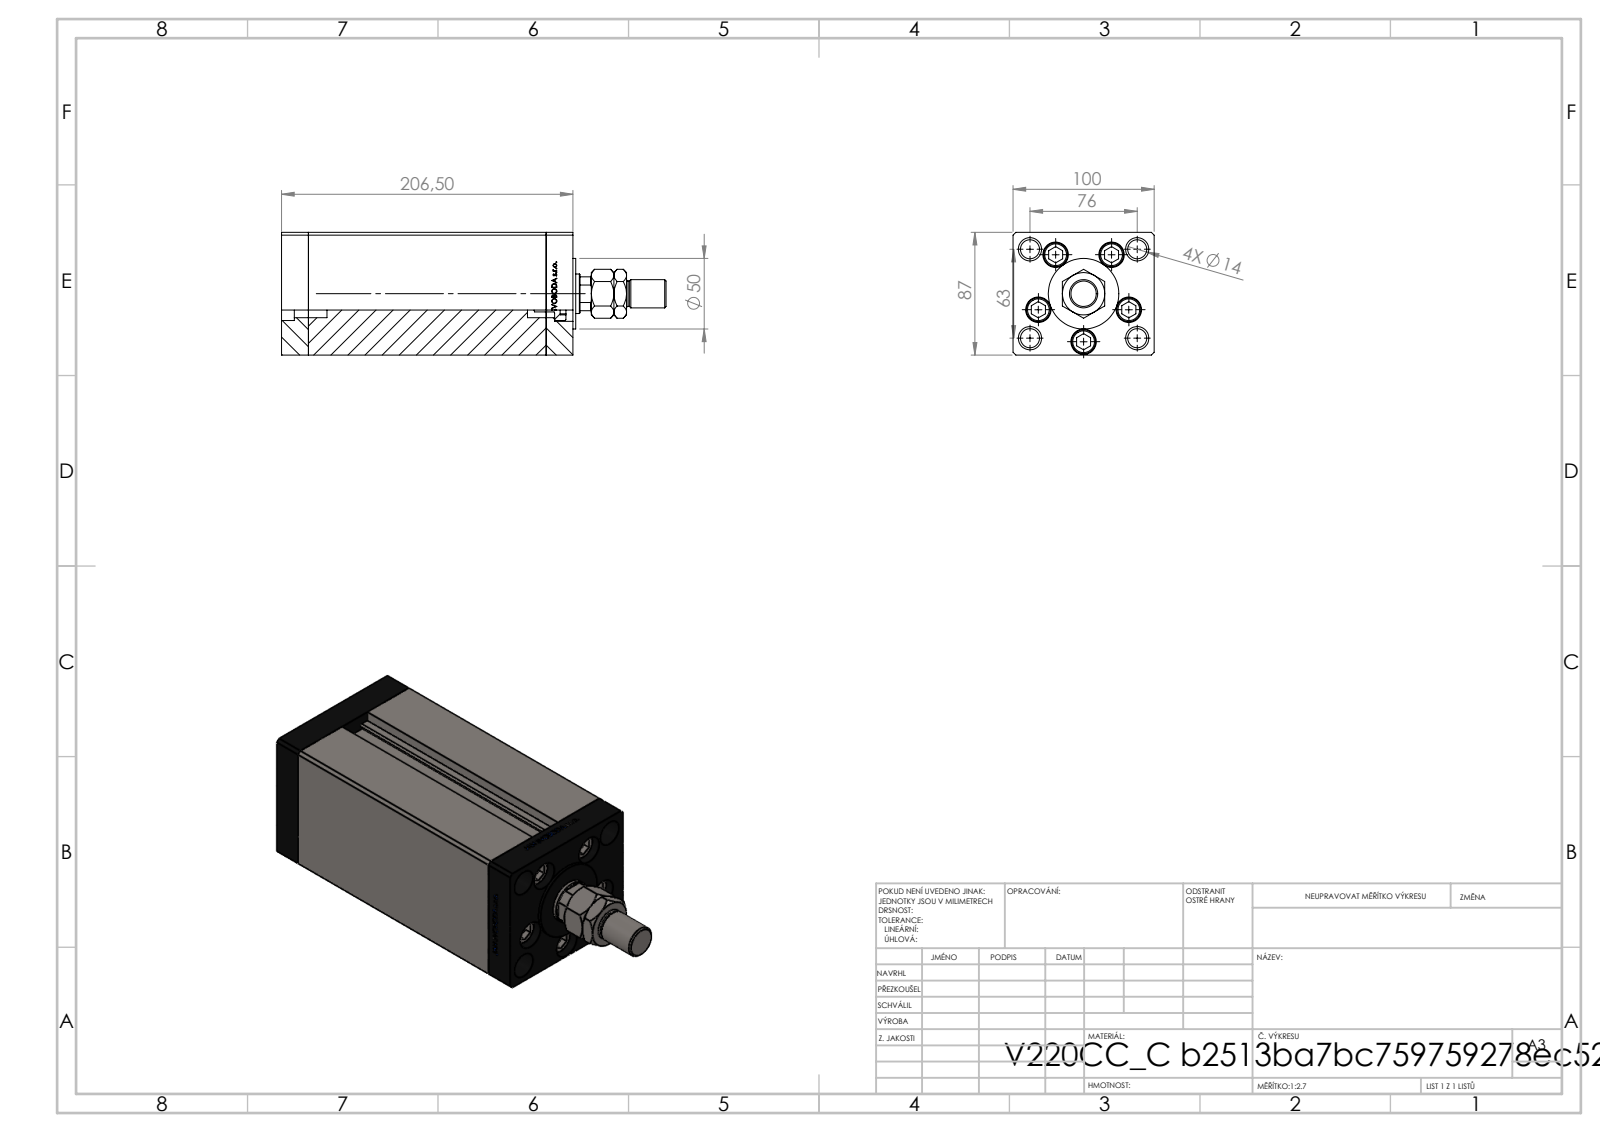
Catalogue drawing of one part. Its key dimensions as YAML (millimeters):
part_name: "V220C_C MIDDLE; V220C FRONT; V220C BACK_C; MTA (+2 more)"
step_written_by: "SolidWorks 2019 (CONFIG_CONTROL_DESIGN)"
units: millimeters
bodies: {solids: 14, faces: 1213, planar: 557, cylindrical: 164, other: 492}
overall_size: [272.5, 100, 87]
volume: 1497000
surface_area: 250961
round_holes:
  - {diameter: 13.5, count: 9}
  - {diameter: 18, count: 5}
  - {diameter: 12, count: 4}
  - {diameter: 16.5, count: 4}
  - {diameter: 17, count: 1}
  - {diameter: 18.5, count: 1}
  - {diameter: 28, count: 1}
round_bosses_or_shafts:
  - {diameter: 8, count: 5}
  - {diameter: 17, count: 4}
  - {diameter: 50, count: 1}
  - {diameter: 20, count: 1}
  - {diameter: 18, count: 1}
partial_cylinders:
  - {radius: 0.93, count: 2}
  - {radius: 13.5, count: 1}
face_to_face_distances: [100, 87, 19, 168.5, 187.5, 34.25, 206.5, 172.25, 153.25, 15.25]
hole_center_spacings: [34, 49.36, 18.59, 21.03, 38.08, 39.27, 40.83, 43.24]
